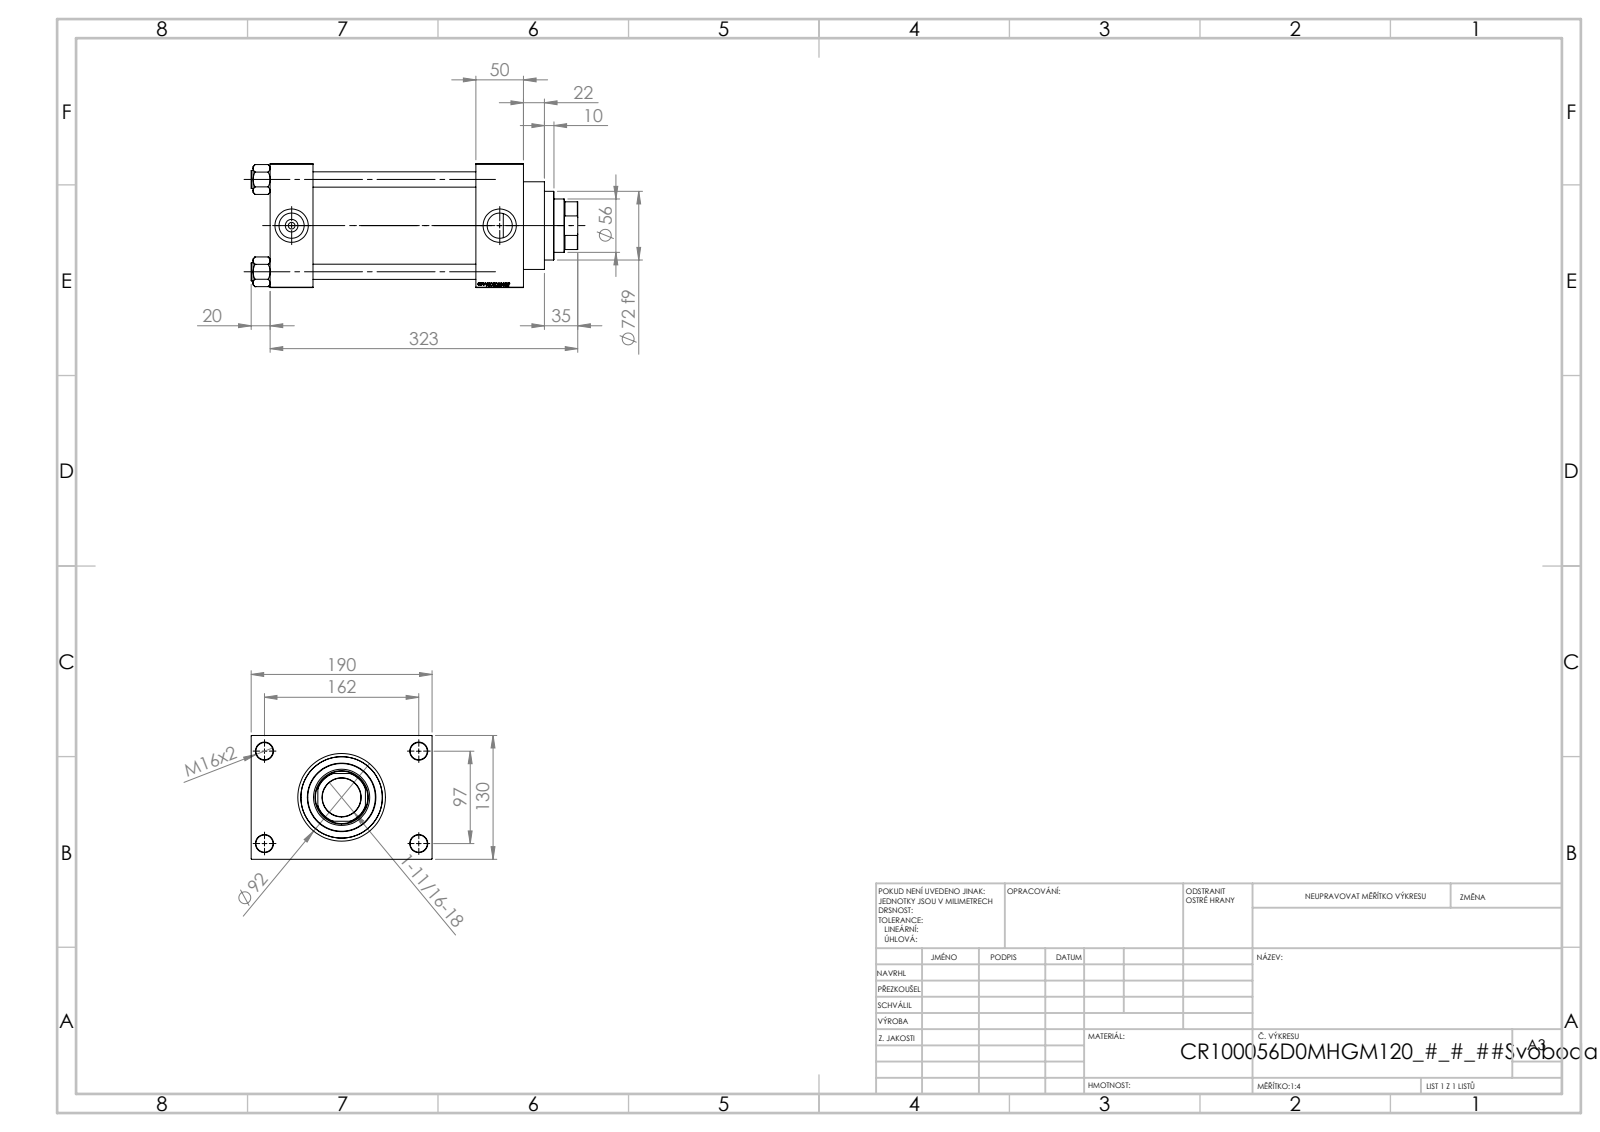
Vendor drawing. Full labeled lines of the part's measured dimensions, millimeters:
Part name (STEP PRODUCT): V215CR_VCP_D; V215CR_D_TYCINKA; V215CR_D_Body; NUT_M5_D (+1 more)
STEP written by: SolidWorks 2019 (CONFIG_CONTROL_DESIGN)
Units: millimetres
Bodies: 11 solids, 1151 faces (545 planar, 88 cylindrical, 518 other)
Overall size (bounding box): 343 × 190 × 130
Volume: 3 052 000 mm³ · Surface area: 464 779 mm²
Round holes (diameter × count): ⌀16 ×4, ⌀18 ×4, ⌀7 ×2, ⌀26.44 ×2, ⌀35 ×2, ⌀40.5 ×1, ⌀56 ×1, ⌀59 ×1, ⌀76 ×1, ⌀85.5 ×1, ⌀100 ×1
Round bosses / shafts (diameter × count): ⌀19 ×4, ⌀106 ×1, ⌀92 ×1, ⌀72 ×1
Partial cylindrical surfaces — rounded edges, fillets, slot ends (radius × count): R27 ×1
Main face-to-face distances: 130, 50, 45, 216, 171, 266, 221, 30, 160, 120
Hole centre spacings: 32.55, 68.52, 94.41, 96.9, 102.27, 129.45, 161.73, 97
